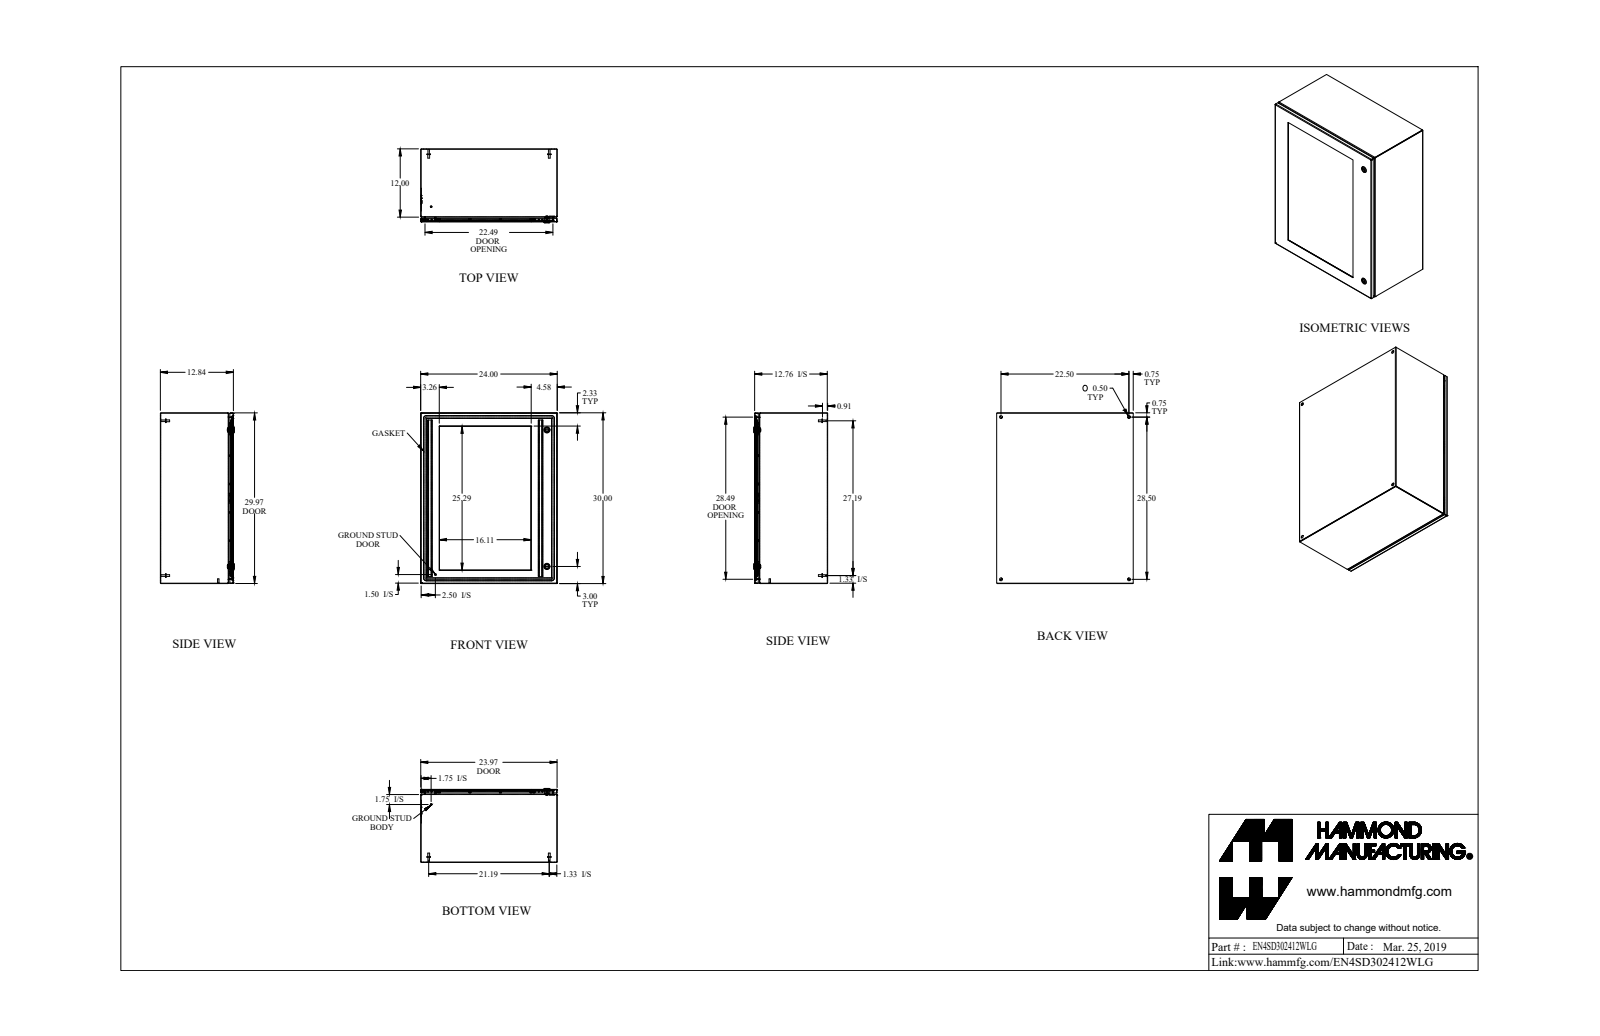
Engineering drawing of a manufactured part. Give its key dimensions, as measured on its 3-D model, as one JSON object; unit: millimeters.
{"part_name": "EN4SD302412WLG", "step_written_by": "SolidWorks 2019 (AUTOMOTIVE_DESIGN)", "units": "millimeters", "bodies": {"solids": 82, "faces": 1605, "planar": 810, "cylindrical": 499, "other": 296}, "overall_size": [762, 609.6, 330.1], "volume_mm3": 5116000, "surface_area_mm2": 4318000, "round_holes": [[3.3, 20], [6.4, 20], [12.7, 4], [5.9, 2], [15.9, 2], [19.9, 2], [4.4, 1], [6.1, 1], [6.1, 1]], "round_bosses_or_shafts": [[5.7, 21], [9.3, 20], [4.2, 20], [15.9, 4], [8, 4], [6.9, 4], [27.9, 2], [13.3, 2]], "partial_cylinders_radius": [[0.9, 14], [2.7, 14], [1.1, 12], [2.1, 12], [3.2, 12], [7.9, 12], [2.5, 8], [0.2, 6]], "face_to_face_distances": [1.8, 324.2, 322.4, 607.8, 760.2, 316.1, 6.4, 317.9, 605.9, 609.6], "hole_center_spacings": [252.7, 503.5, 126.4, 136.4, 422.8, 435.5, 453.4, 682.6]}
